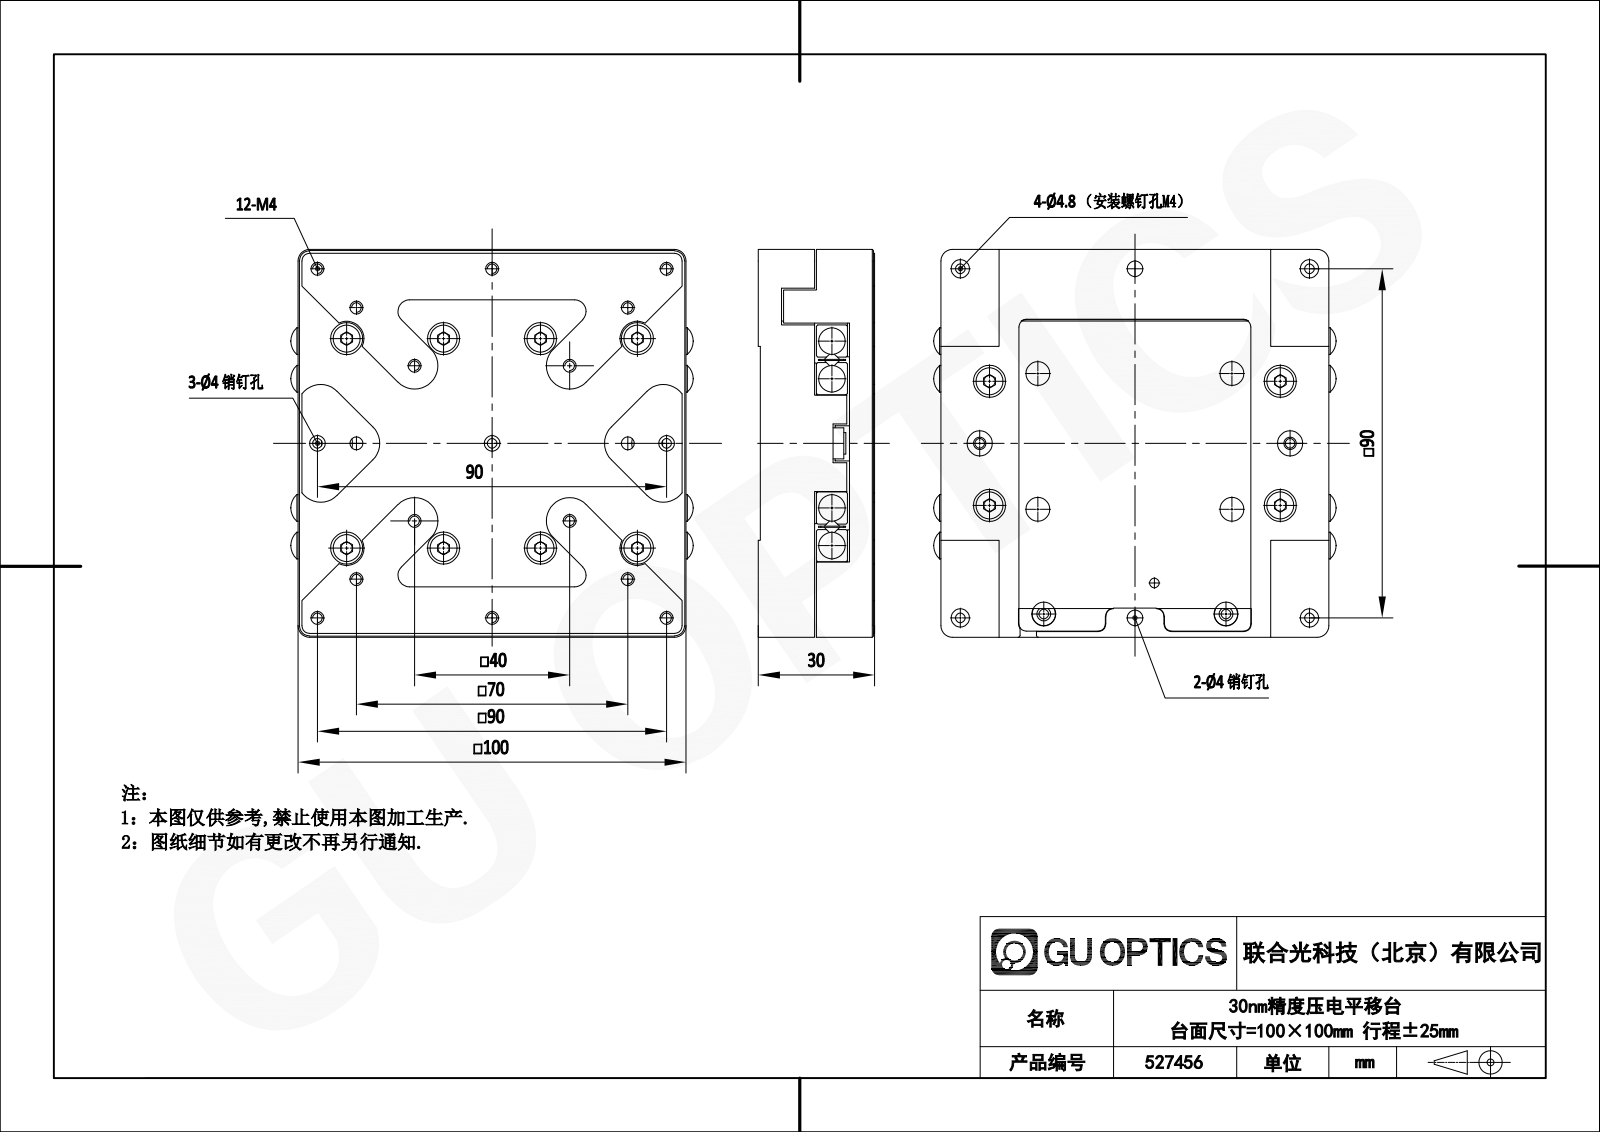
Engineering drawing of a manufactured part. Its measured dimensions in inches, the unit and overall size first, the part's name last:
Units: inches
Overall size (bounding box): 4.087 × 3.937 × 1.181
Round holes (diameter × count): ⌀0.098 ×22, ⌀0.177 ×18, ⌀0.13 ×16, ⌀0.134 ×16, ⌀0.236 ×16, ⌀0.325 ×16, ⌀0.142 ×6, ⌀0.244 ×6, ⌀0.157 ×5, ⌀0.138 ×4, ⌀0.189 ×4, ⌀0.102 ×2
Round bosses / shafts (diameter × count): ⌀0.118 ×28, ⌀0.276 ×12, ⌀0.157 ×12, ⌀0.272 ×4, ⌀0.217 ×2
Partial cylindrical surfaces — rounded edges, fillets, slot ends (radius × count): R0.098 ×34, R0.118 ×19, R0.079 ×14, R0.236 ×10, R0.075 ×6, R0.031 ×4, R0.039 ×4, R0.058 ×4
Main face-to-face distances: 0.02, 0.335, 0.354, 0.571, 0.244, 0.906, 1.15, 0.591, 0.327, 0.551
Hole centre spacings: 0.984, 1.075, 1.958, 1.969, 0.433, 0.637, 1.068, 1.693
Volume: 17.78 in³ · Surface area: 153.5 in²
Bodies: 25 solids, 1403 faces (640 planar, 553 cylindrical, 210 other)
Part name (STEP PRODUCT): VR3_14Z_BCJ.STEP; VR3_100_GD.STEP; DG_LS3-1050-JCEL-401.STEP; VR3-100x14Z.STEP (+7 more)
STEP written by: SolidWorks 2020 (CONFIG_CONTROL_DESIGN)
